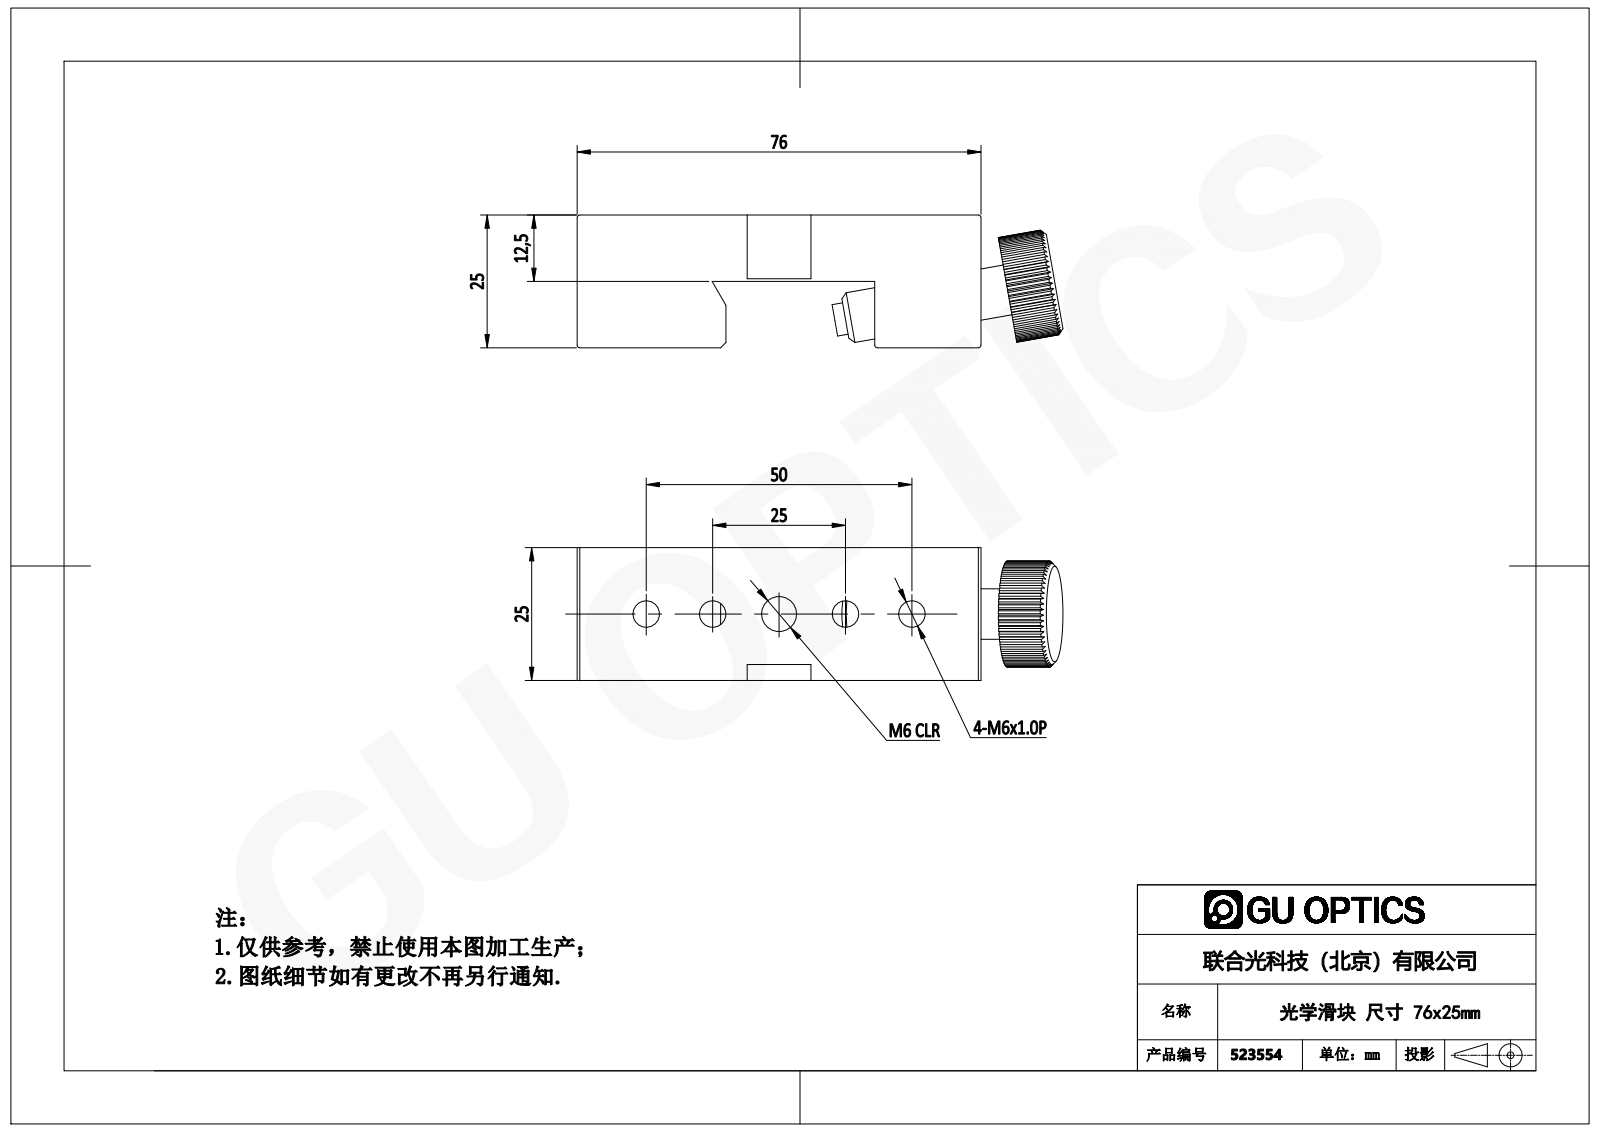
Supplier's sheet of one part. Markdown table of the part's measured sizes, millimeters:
| quantity | value |
| --- | --- |
| part name | CR-3 |
| STEP written by | SolidWorks 2012 (CONFIG_CONTROL_DESIGN) |
| units | millimeters |
| bodies | 0 solids, 208 faces (134 planar, 72 cylindrical, 2 other) |
| overall size | 91.42 × 25 × 25 |
| round holes (diameter × count) | 5 × 4, 11 × 2, 6.5 × 1, 6.6 × 1 |
| round bosses / shafts (diameter × count) | 9.5 × 1, 6 × 1 |
| partial cylindrical surfaces (radius × count) | 0.5 × 5, 10 × 1 |
| main face-to-face distances | 25, 12.5, 76, 28, 56, 20, 9, 48, 9.5, 9.51 |
| hole center spacings | 12.5, 25, 37.5, 50 |
